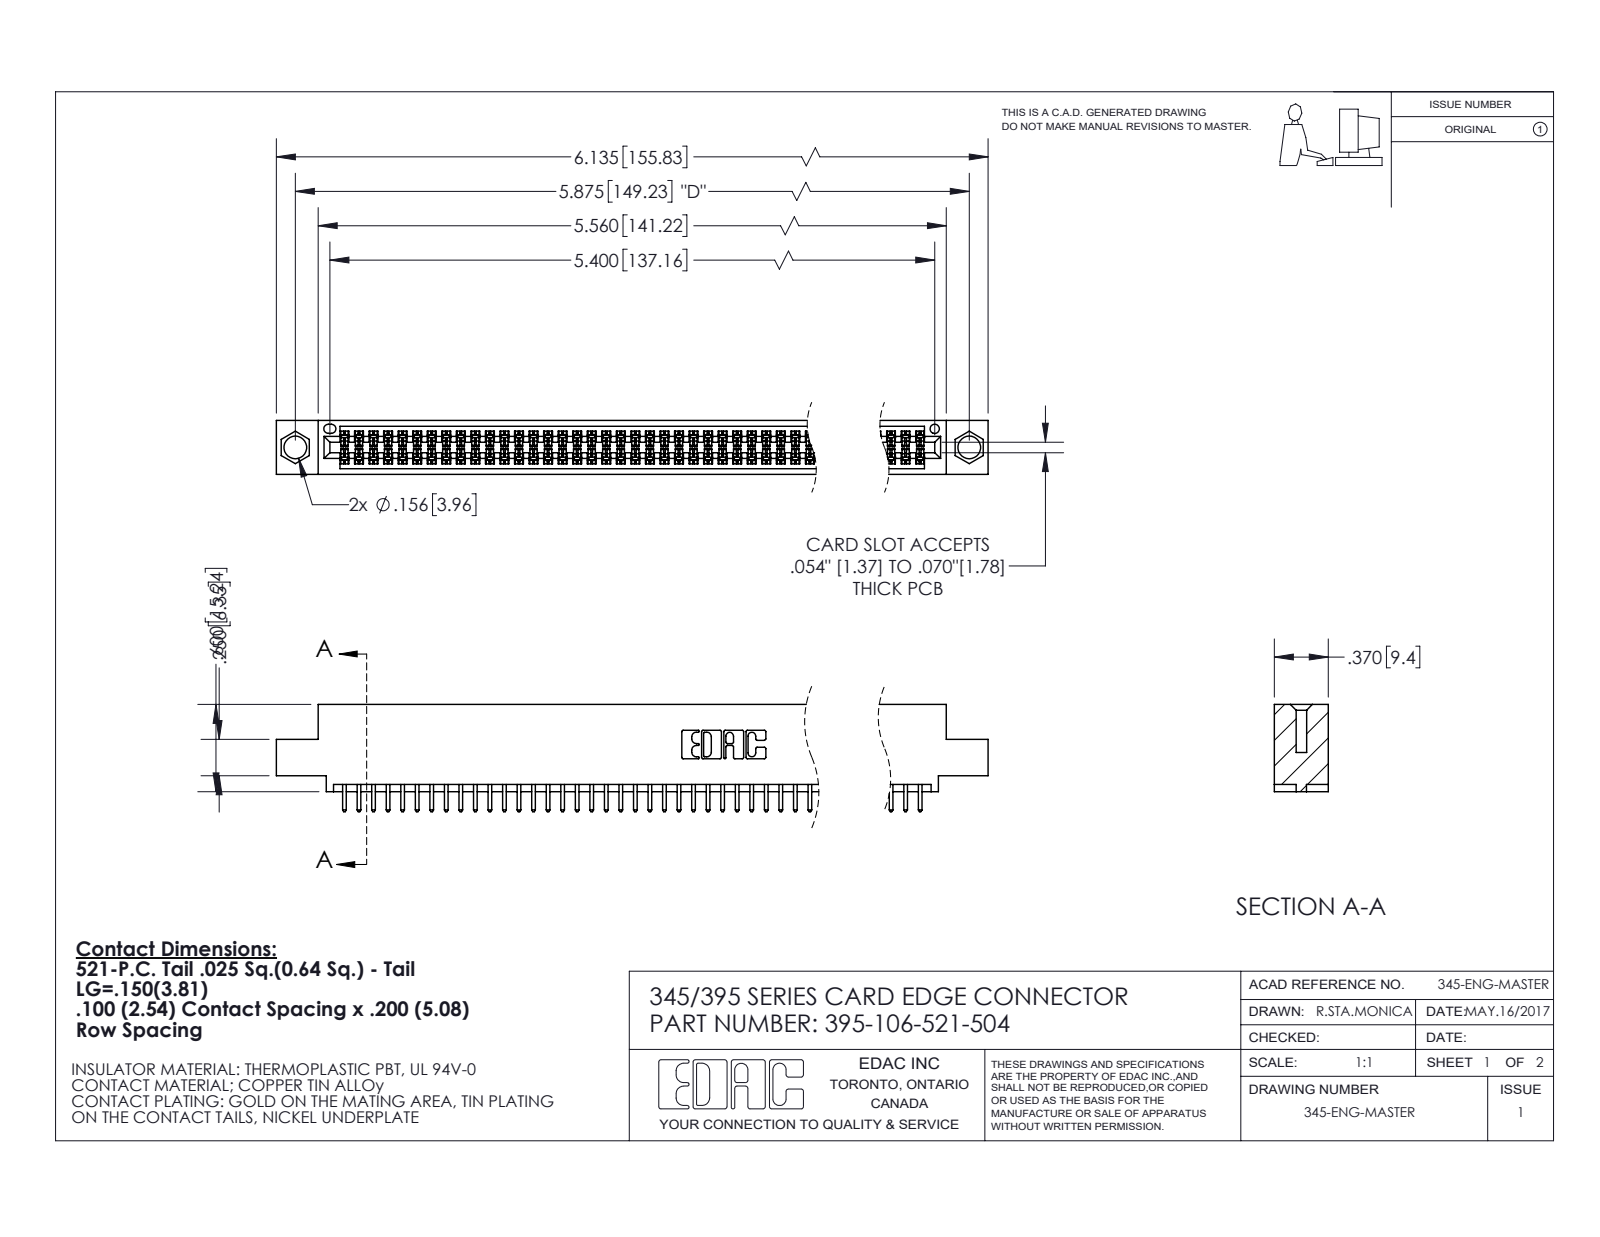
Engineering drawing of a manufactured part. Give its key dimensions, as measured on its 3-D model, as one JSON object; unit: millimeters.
{"part_name": "395-106-521-504; 345 Part_0.110 Offset - 0.156 Dia-TI; 345-292-001_345-293-121", "step_written_by": "SolidWorks 2020 (CONFIG_CONTROL_DESIGN)", "units": "millimeters", "bodies": {"solids": 107, "faces": 5444, "planar": 3596, "cylindrical": 1848, "other": 0}, "overall_size": [155.8, 18.7, 9.4], "volume_mm3": 15000, "surface_area_mm2": 22070, "round_holes": [[4, 2], [1.6, 1]], "partial_cylinders_radius": [[0.2, 159], [0.3, 106], [0.3, 22], [0.2, 6], [0.8, 6], [0.7, 3], [0.4, 2], [0.5, 2]], "face_to_face_distances": [7.6, 1.8, 5.1, 2.5, 6.9, 0.6, 9.4, 5.7, 4.4, 3.8], "hole_center_spacings": [6.9, 143.2, 149.2]}
